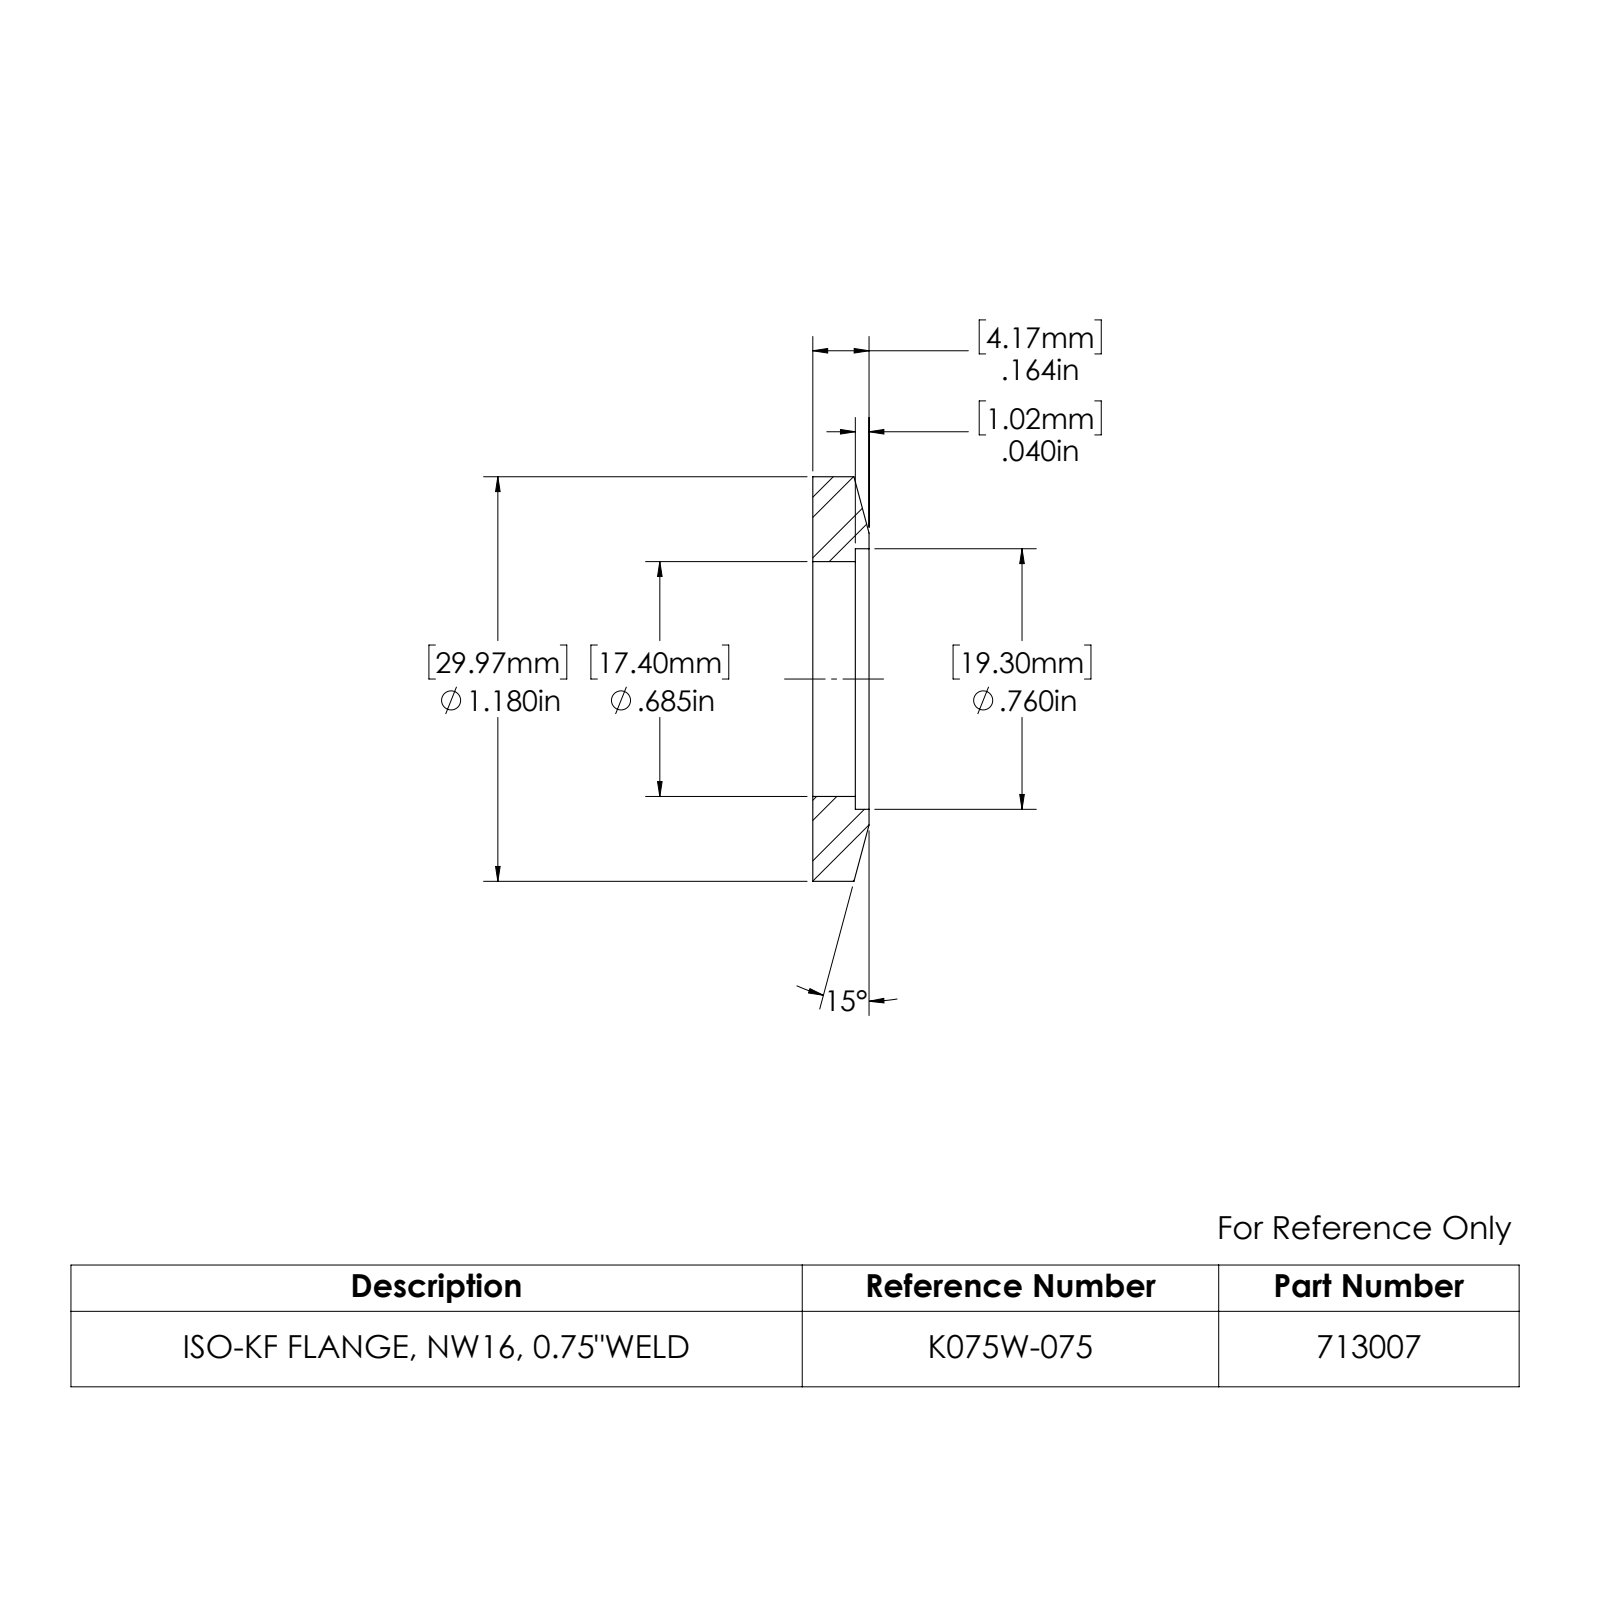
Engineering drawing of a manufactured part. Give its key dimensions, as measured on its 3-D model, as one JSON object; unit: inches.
{"part_name": "713007", "step_written_by": "SolidWorks 2022 (AUTOMOTIVE_DESIGN)", "units": "inches", "bodies": {"solids": 1, "faces": 11, "planar": 3, "cylindrical": 6, "other": 2}, "overall_size": [1.18, 1.18, 0.164], "volume_in3": 0.103, "surface_area_in2": 2.276, "round_holes": [[0.685, 1], [0.76, 1]], "round_bosses_or_shafts": [[1.18, 1]], "face_to_face_distances": [0.164, 0.04, 0.124]}
